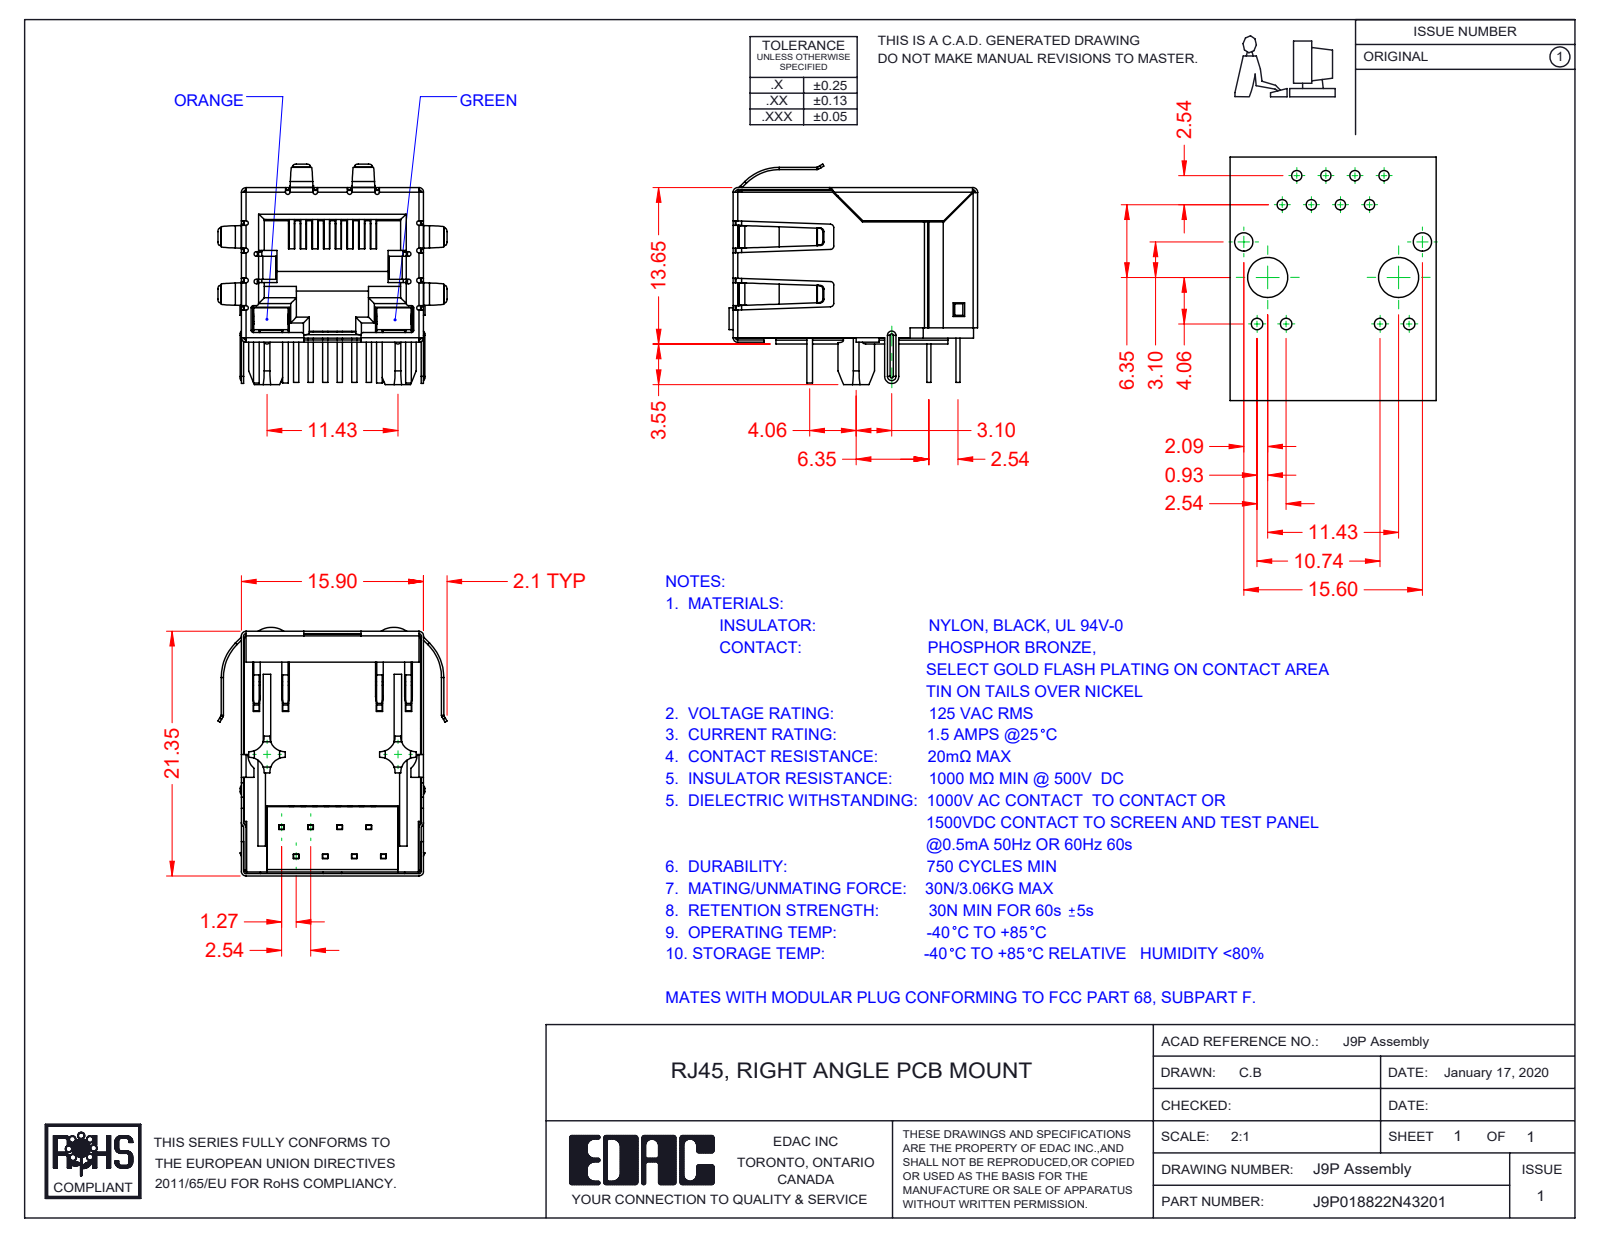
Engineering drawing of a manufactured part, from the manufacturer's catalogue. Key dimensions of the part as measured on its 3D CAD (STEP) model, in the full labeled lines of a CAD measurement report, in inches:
Part name (STEP PRODUCT): 9P-LED Assembly; J9P018822N43202; 9P-LED Contact Lock; 9P-LED Shield (+4 more)
STEP written by: SolidWorks 2016 (CONFIG_CONTROL_DESIGN)
Units: inches
Bodies: 13 solids, 1472 faces (1042 planar, 336 cylindrical, 94 other)
Overall size (bounding box): 0.854 × 0.787 × 0.758
Volume: 0.164 in³ · Surface area: 11.65 in²
Partial cylindrical surfaces — rounded edges, fillets, slot ends (radius × count): R0.008 ×39, R0.02 ×22, R0.012 ×20, R0.016 ×16, R0.051 ×8, R0.009 ×5, R0.004 ×4, R0.012 ×4
Main face-to-face distances: 0.608, 0.618, 0.616, 0.014, 0.021, 0.61, 0.487, 0.024, 0.055, 0.023
